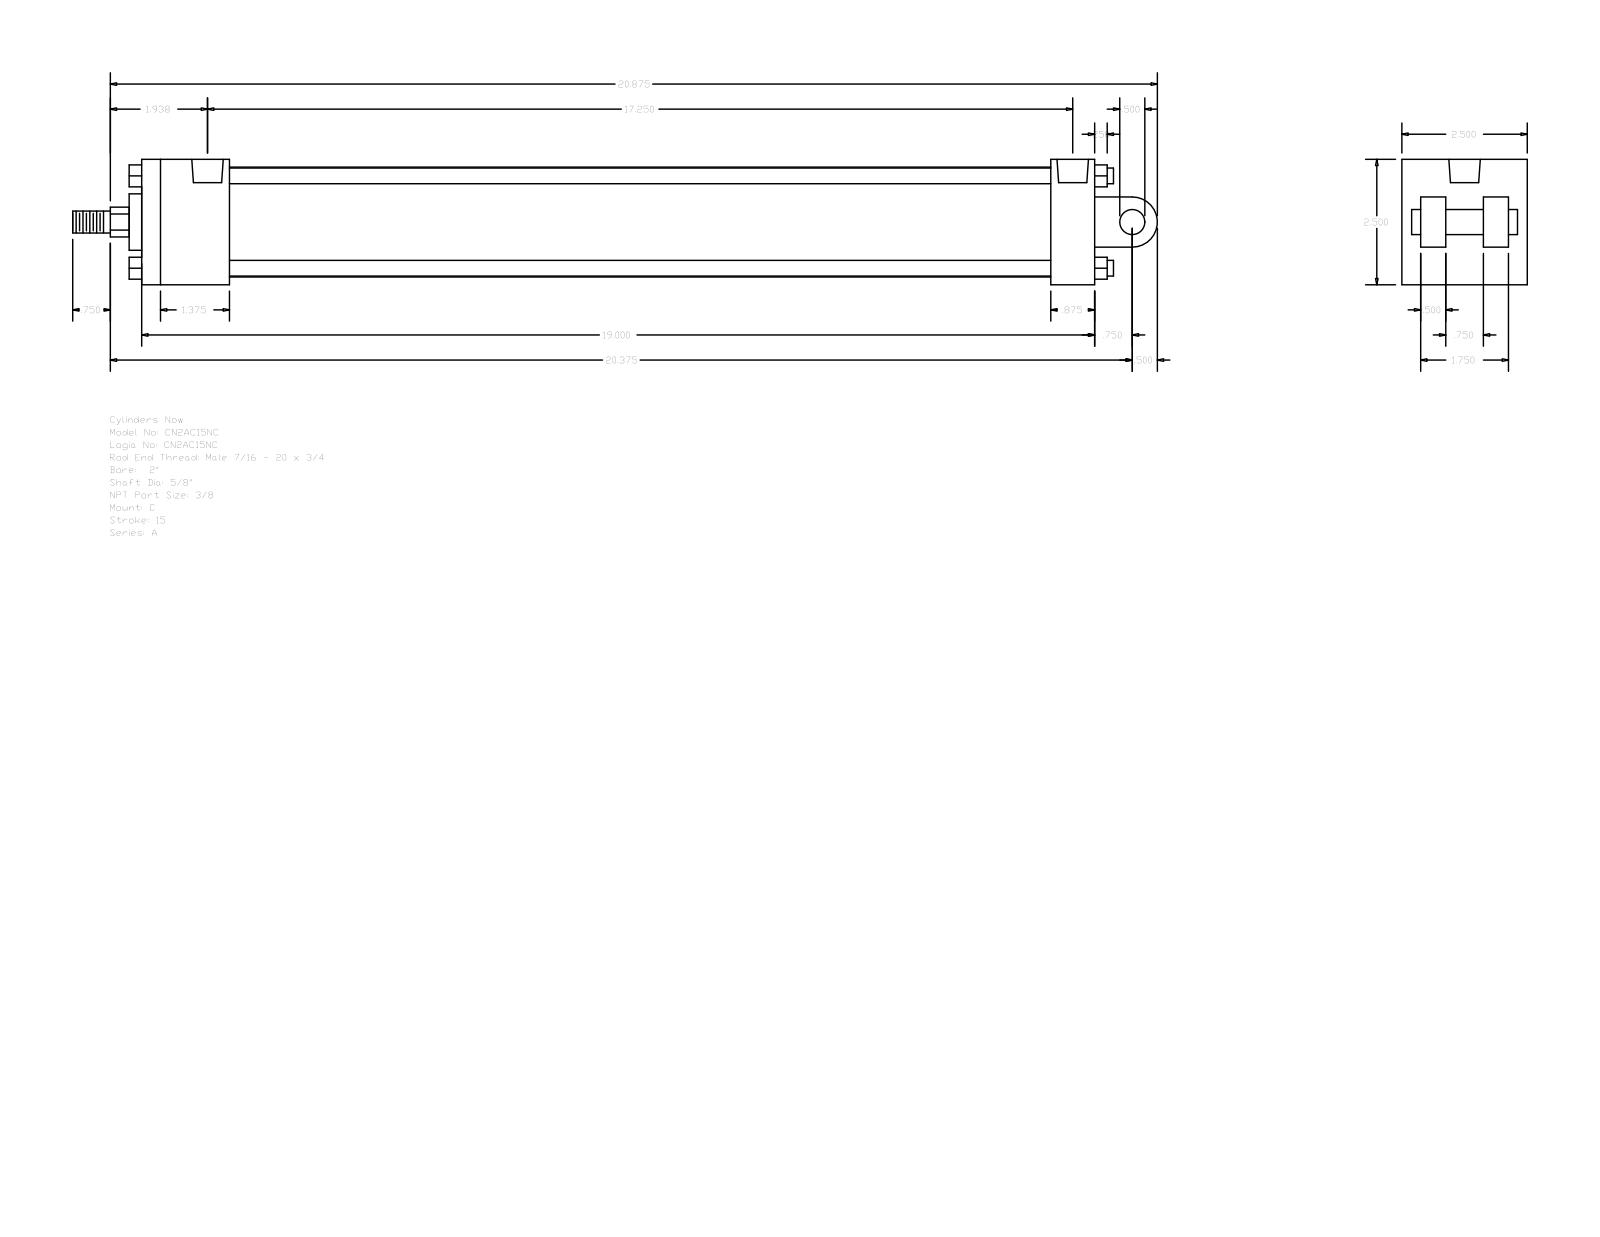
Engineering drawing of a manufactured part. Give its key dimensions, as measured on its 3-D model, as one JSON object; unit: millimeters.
{"part_name": "A_C__0200_0.625", "step_written_by": "GSSL Pune (CONFIG_CONTROL_DESIGN)", "units": "millimeters", "bodies": {"solids": 0, "faces": 135, "planar": 102, "cylindrical": 33, "other": 0}, "overall_size": [549.27, 63.5, 63.5], "round_holes": [[5.56, 4], [15.93, 2]], "round_bosses_or_shafts": [[7.94, 4], [55.63, 1], [28.57, 1], [15.88, 1], [12.7, 1], [11.11, 1]], "partial_cylinders_radius": [[7.54, 1], [12.7, 1]], "face_to_face_distances": [63.5, 482.6, 44.45, 9.52, 438.15, 460.37, 415.92, 22.23, 12.7, 53.98], "hole_center_spacings": [430.2, 3.97, 3.98, 434.17, 434.18, 438.15]}
